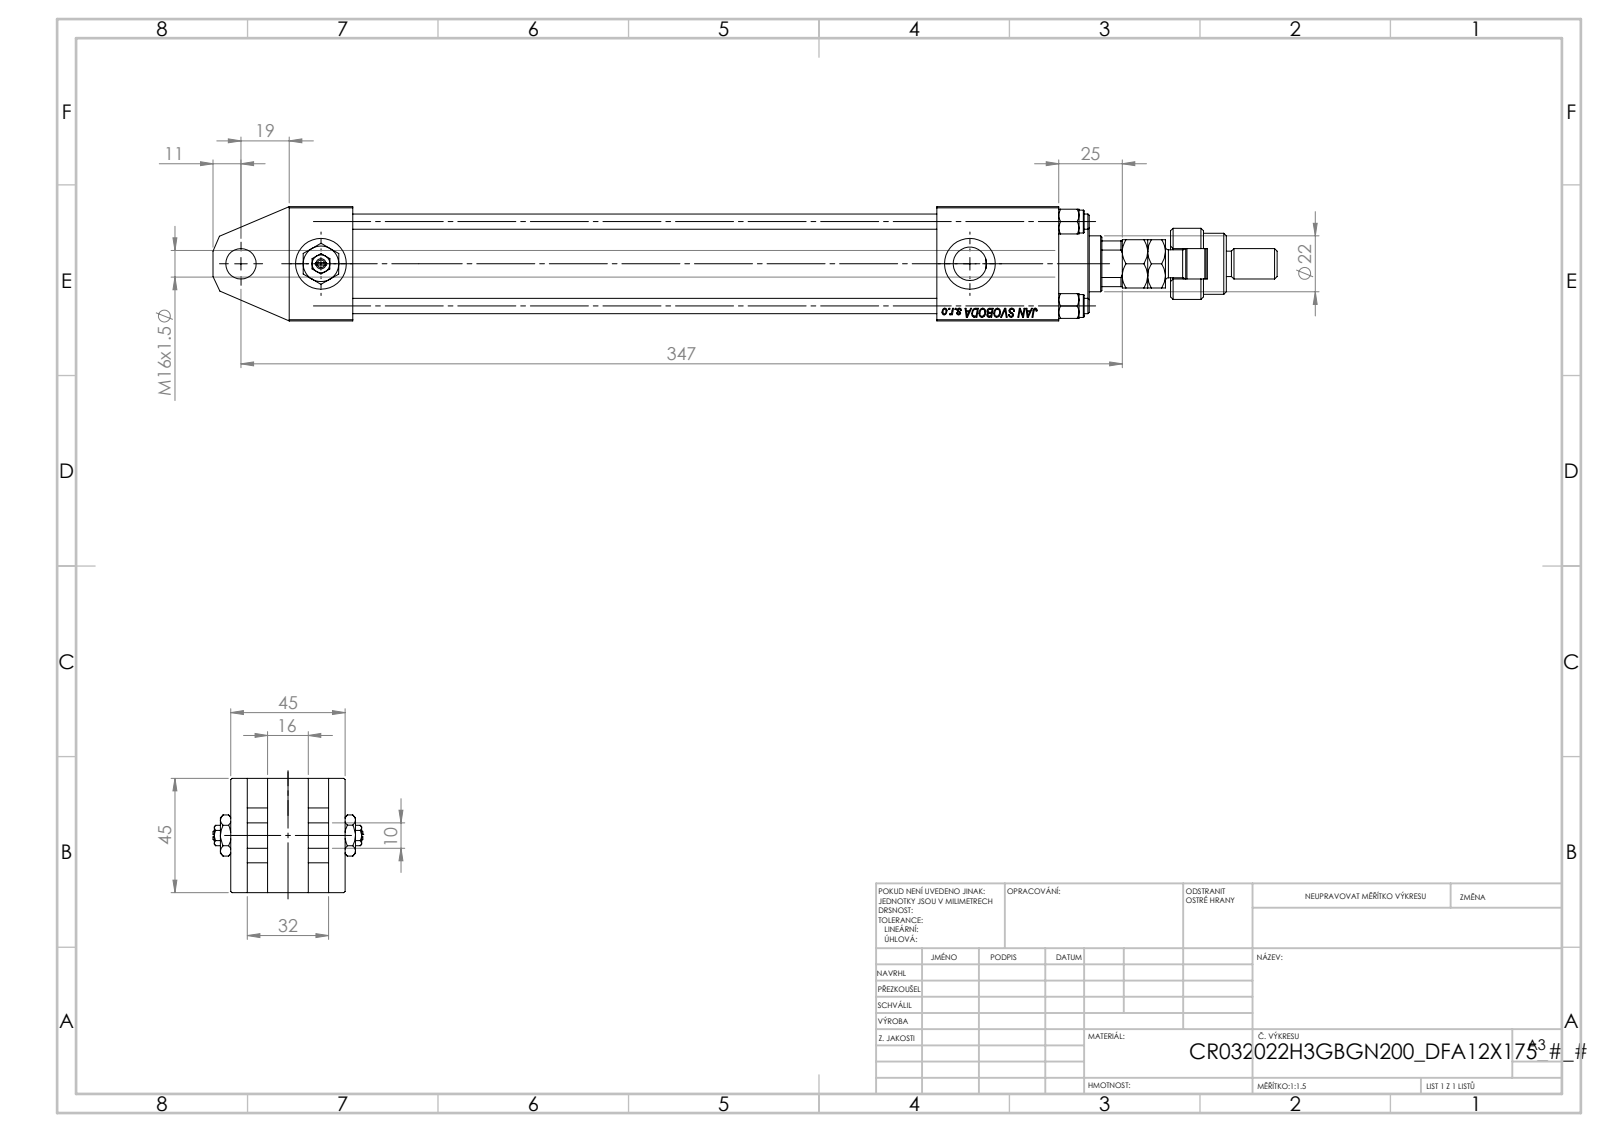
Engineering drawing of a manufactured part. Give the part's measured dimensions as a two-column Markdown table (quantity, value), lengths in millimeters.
| quantity | value |
| --- | --- |
| part name | V215CR_H_Body; V215CR_TYCINKA_H; Zatka_pro_OIL_PORT; V215_VC_A (+4 more) |
| STEP written by | SolidWorks 2019 (CONFIG_CONTROL_DESIGN) |
| units | millimeters |
| bodies | 15 solids, 1321 faces (592 planar, 111 cylindrical, 618 other) |
| overall size | 419 × 59 × 45 |
| volume | 389 227 mm³ |
| surface area | 153 129 mm² |
| round holes (diameter × count) | 6 × 4, 2.5 × 2, 7 × 2, 13.16 × 2, 20 × 2, 10.5 × 1, 12 × 1, 22 × 1, 24 × 1, 25 × 1, 32 × 1, 33 × 1 |
| round bosses / shafts (diameter × count) | 9 × 4, 38 × 1, 34 × 1, 28 × 1, 18 × 1, 12 × 1, 11 × 1, 10 × 1 |
| partial cylindrical surfaces (radius × count) | 9.75 × 1, 10.5 × 1 |
| main face-to-face distances | 45, 8, 25, 14.5, 24, 6.5, 38.5, 30.5, 303, 230 |
| hole center spacings | 16.7, 23.48, 33.2, 35.47, 14.75, 46.95, 29.5, 31.5 |
